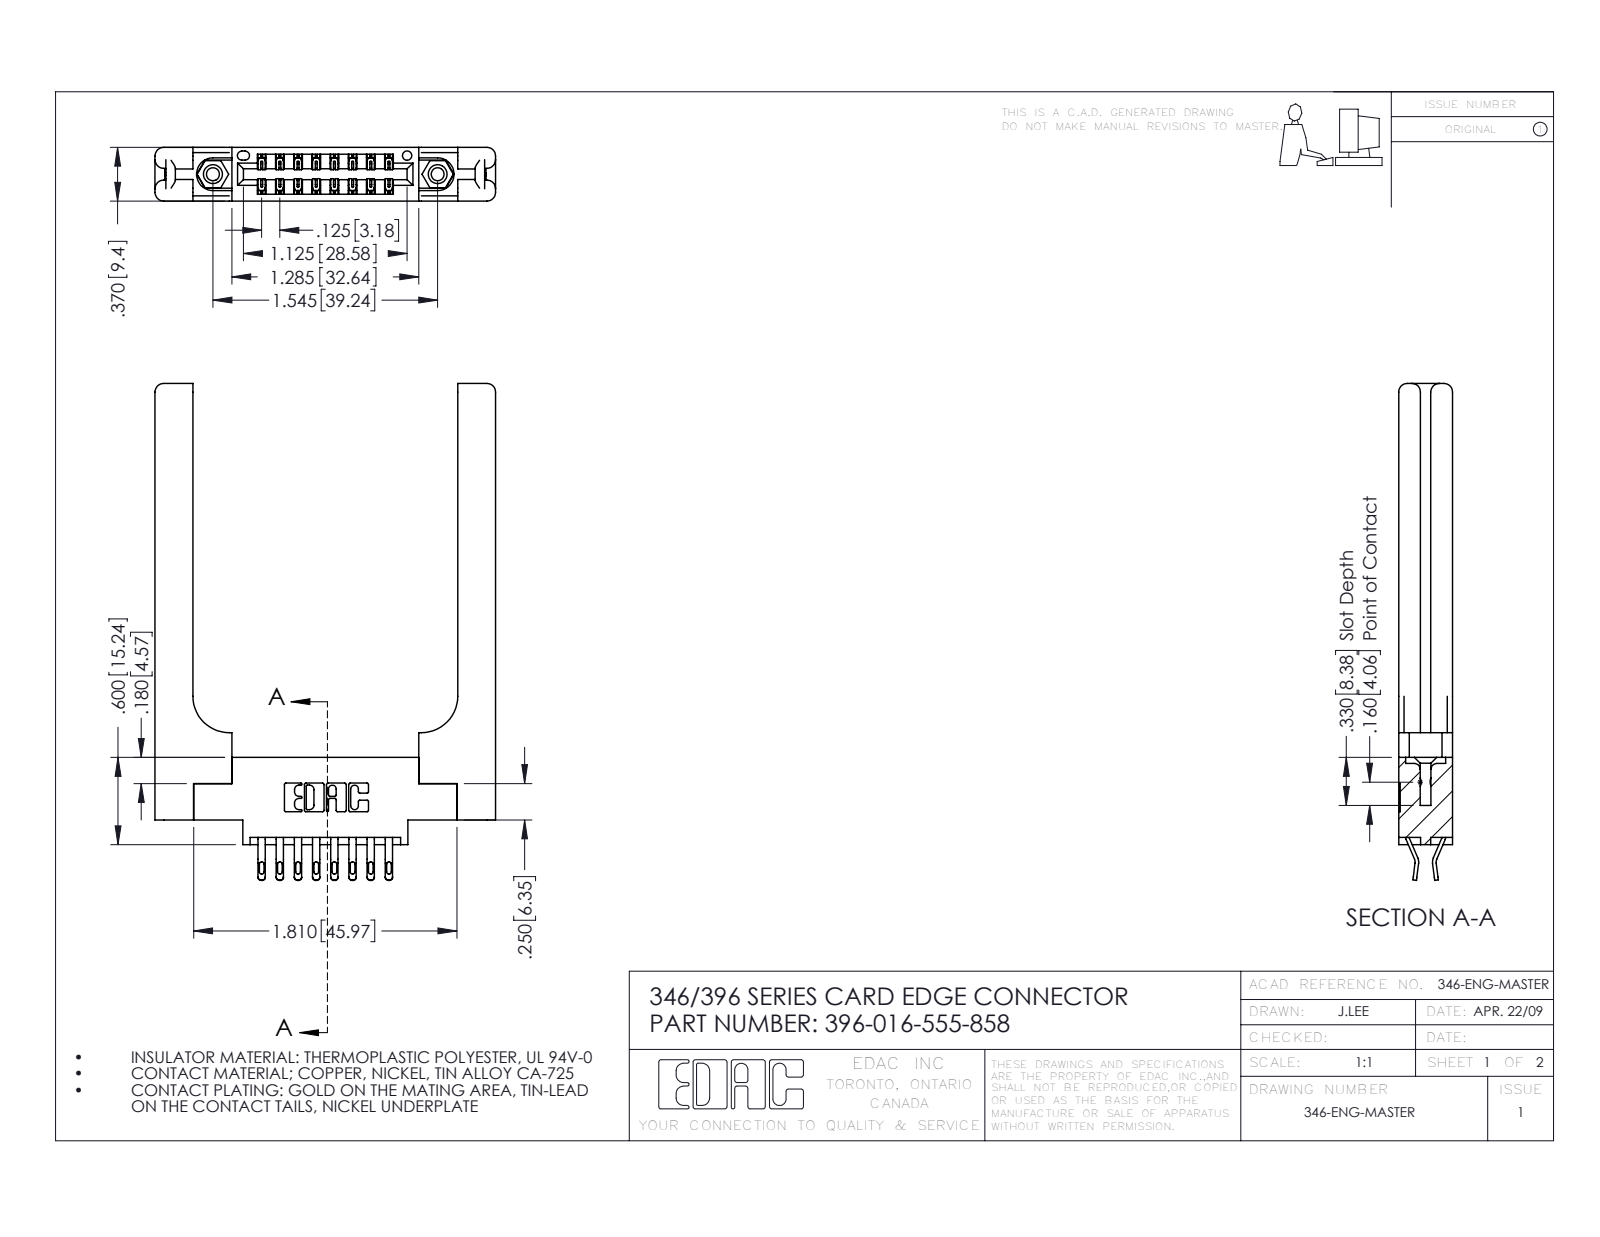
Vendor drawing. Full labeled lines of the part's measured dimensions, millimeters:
Part name (STEP PRODUCT): 346-220-058_345-220-058; 346 Part_0.170 Offset - 0.156 Dia-TH; 396-016-555-858; 345-292-001_555 Tail (+1 more)
STEP written by: SolidWorks 2016 (CONFIG_CONTROL_DESIGN)
Units: millimetres
Bodies: 21 solids, 1310 faces (756 planar, 494 cylindrical, 60 other)
Overall size (bounding box): 86.7 × 59.5 × 9.4
Volume: 12 900 mm³ · Surface area: 12 240 mm²
Round holes (diameter × count): ⌀2.3 ×2, ⌀3.2 ×2, ⌀4 ×2, ⌀1.6 ×1
Round bosses / shafts (diameter × count): ⌀3.9 ×2
Partial cylindrical surfaces — rounded edges, fillets, slot ends (radius × count): R0.4 ×32, R0.5 ×32, R0.2 ×24, R0.3 ×22, R1.5 ×16, R0.2 ×6, R0.8 ×6, R0.7 ×3
Main face-to-face distances: 9.4, 3.8, 5.6, 1.8, 3.8, 6.4, 2.6, 1.2, 8.2, 4.4
Hole centre spacings: 6.2, 34.1, 39.2
